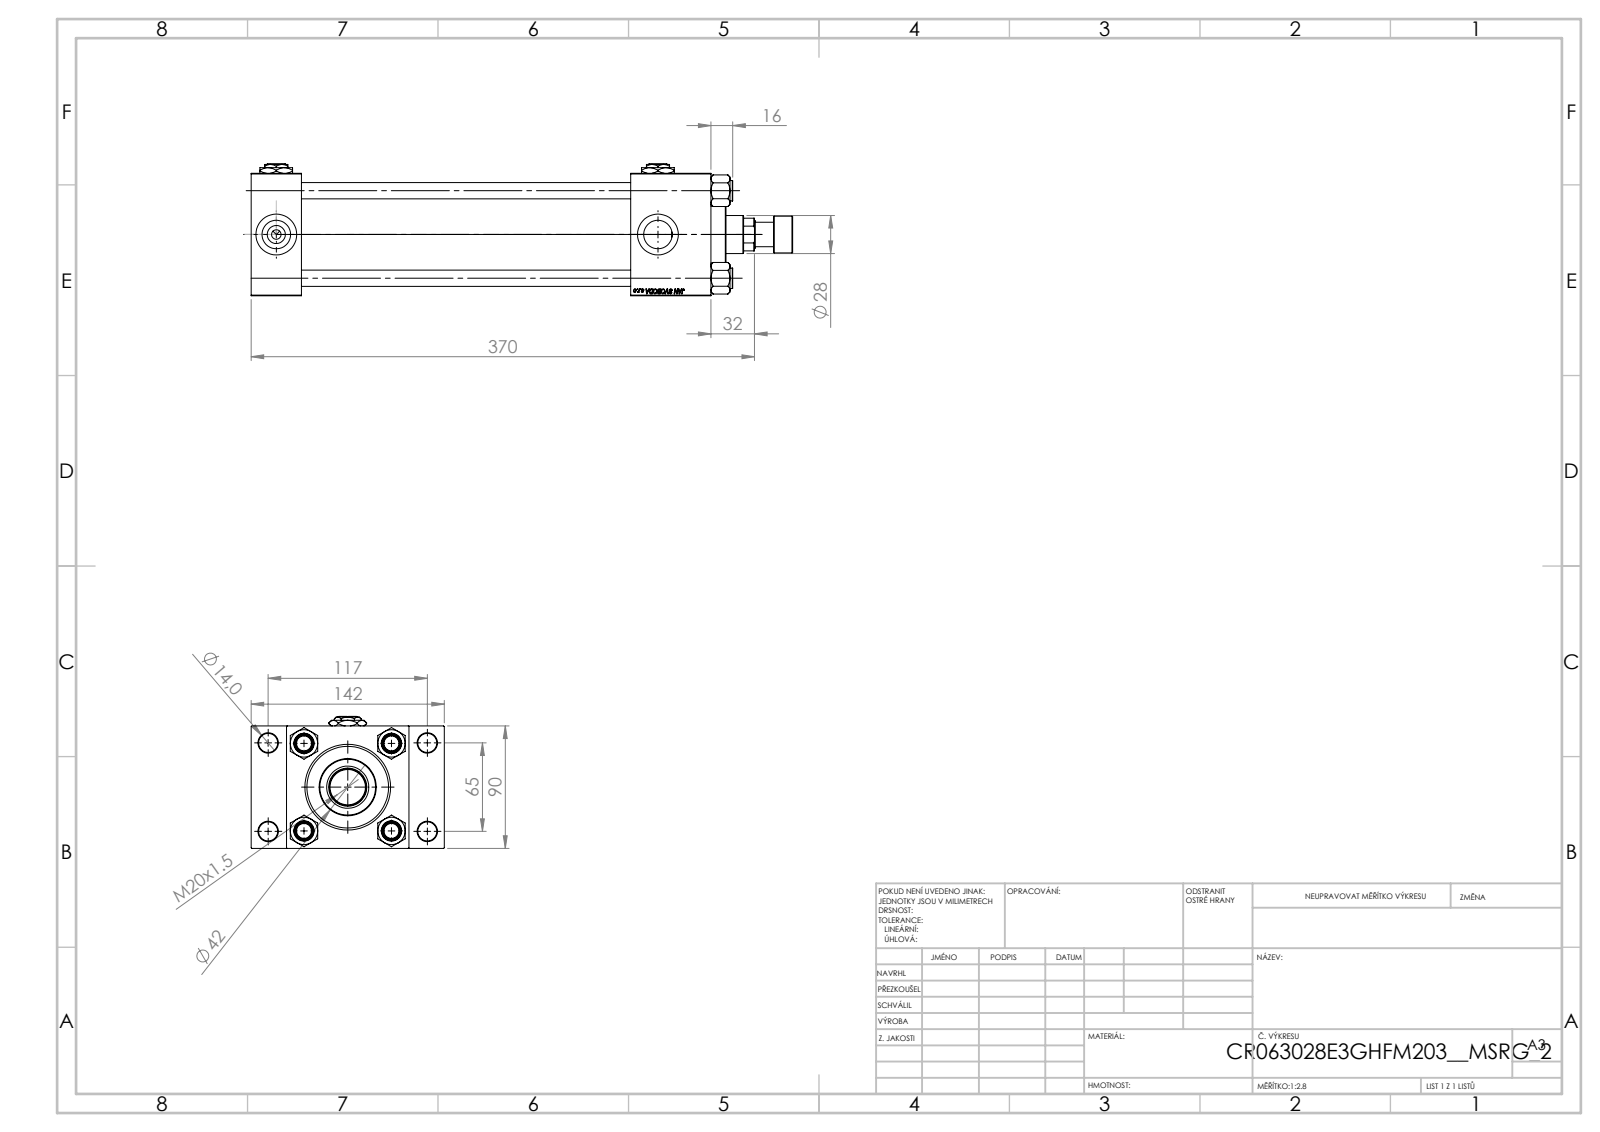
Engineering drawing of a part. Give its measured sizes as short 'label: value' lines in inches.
name: V215CR_TYCINKA_E; Zatka_pro_OIL_PORT; NUT_M5_E; V215CR_VCP_E (+3 more)
written by: SolidWorks 2019 (CONFIG_CONTROL_DESIGN)
unit: in
bodies: 14 solids, 1251 faces (550 planar, 101 cylindrical, 600 other)
size: 15.669 × 5.591 × 3.819
volume: 86.59 in³; area: 518.1 in²
holes: 4× ⌀0.472, 4× ⌀0.551, 4× ⌀0.825, 4× ⌀1.181, 3× ⌀0.276, 1× ⌀0.728, 1× ⌀1.102, 1× ⌀1.22, 1× ⌀1.969, 1× ⌀2.362, 1× ⌀2.48
bosses: 4× ⌀0.591, 1× ⌀2.717, 1× ⌀1.654, 1× ⌀1.063, 1× ⌀0.709
face distances: 3.543, 1.457, 13.307, 11.85, 1.024, 4.567, 2.323, 10.984, 9.528, 12.177
hole spacings: 1.037, 1.79, 2.531, 2.635, 2.748, 3.569, 4.383, 2.559
